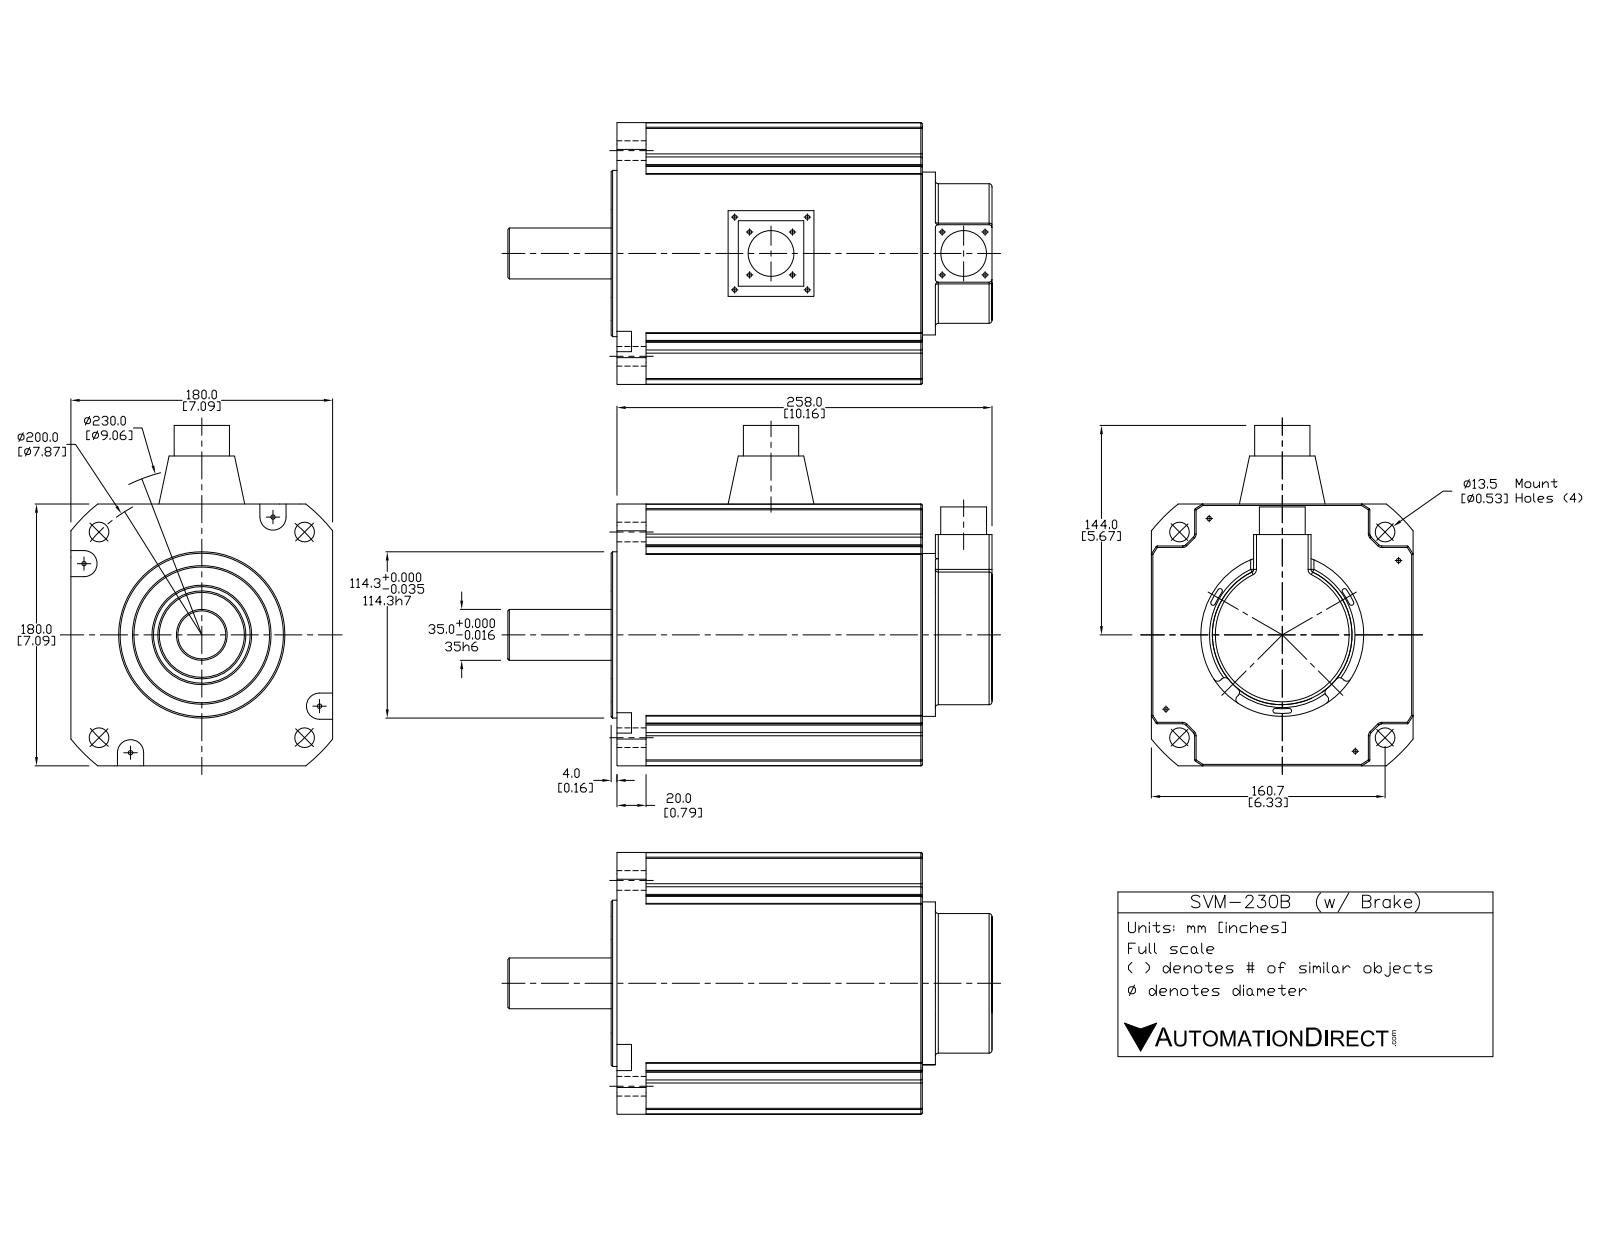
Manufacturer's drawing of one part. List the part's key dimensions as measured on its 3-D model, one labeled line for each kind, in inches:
Part name (STEP PRODUCT): SVM-230B
STEP written by: SolidWorks 2015 (AUTOMOTIVE_DESIGN)
Units: inches
Bodies: 32 solids, 460 faces (238 planar, 135 cylindrical, 87 other)
Overall size (bounding box): 13.11 × 9.213 × 7.087
Volume: 404.3 in³ · Surface area: 650.1 in²
Round holes (diameter × count): ⌀0.531 ×4, ⌀1.063 ×1, ⌀1.311 ×1, ⌀3.701 ×1
Round bosses / shafts (diameter × count): ⌀0.079 ×17, ⌀0.094 ×6, ⌀0.63 ×4, ⌀0.142 ×3, ⌀4.498 ×1, ⌀4.409 ×1, ⌀3.78 ×1, ⌀2.638 ×1
Partial cylindrical surfaces — rounded edges, fillets, slot ends (radius × count): R0.197 ×8, R0.039 ×4, R0.157 ×4, R0.236 ×4, R0.354 ×4, R2.559 ×1, R4.528 ×1
Main face-to-face distances: 6.496, 7.087, 1.219, 7.283, 0.787, 0.709, 0.609, 5.913, 1.173, 7.205
Hole centre spacings: 3.937, 5.568, 7.874, 5.291
